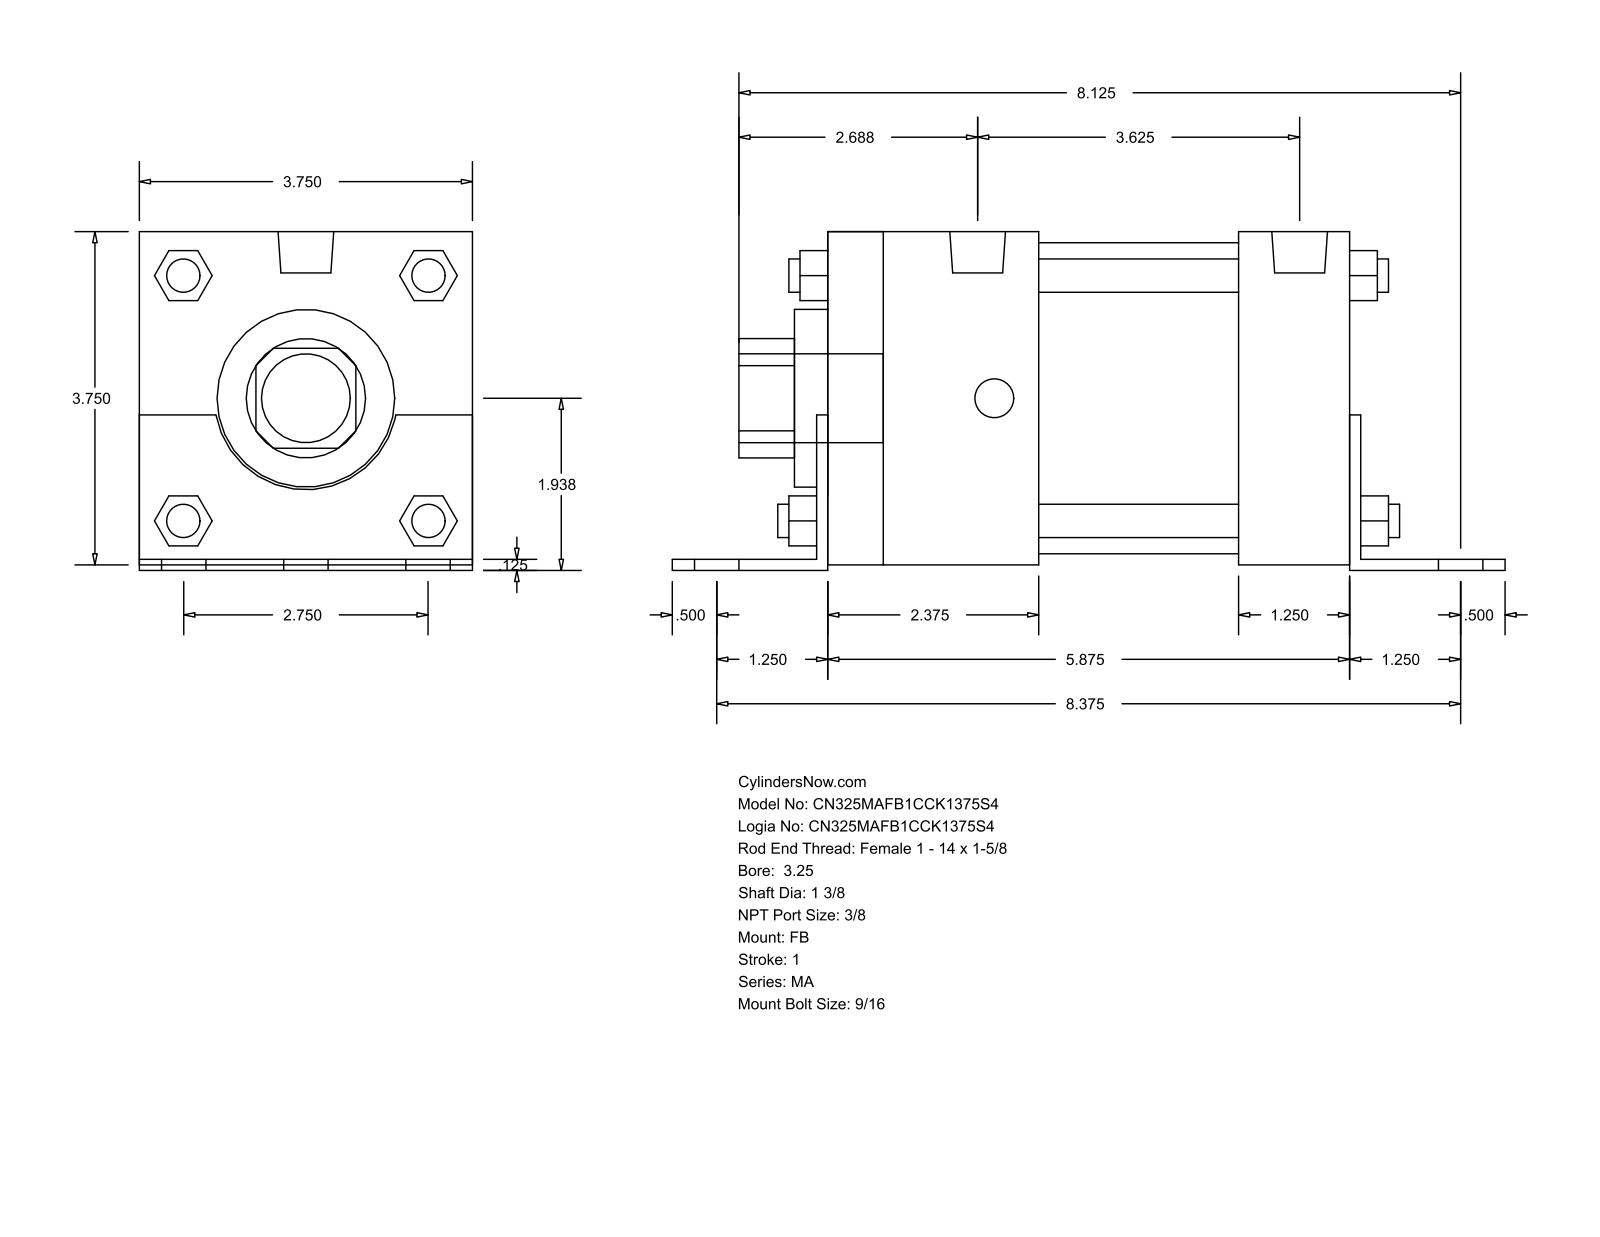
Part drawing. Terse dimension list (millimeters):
name: MA_FB__0325_1.375
written by: GSSL Pune (CONFIG_CONTROL_DESIGN)
unit: mm
bodies: 0 solids, 140 faces (105 planar, 35 cylindrical, 0 other)
size: 238.12 × 96.84 × 95.25
holes: 1× ⌀34.92, 1× ⌀50.8, 1× ⌀88.9
bosses: 6× ⌀14.29, 4× ⌀11.11, 4× ⌀9.53, 2× ⌀15.93, 1× ⌀25.4
rounds: 1× R17.06, 1× R26.16
face distances: 95.24, 3.17, 1.59, 96.83, 1.58, 93.66, 3.18, 149.22, 152.4, 60.32
